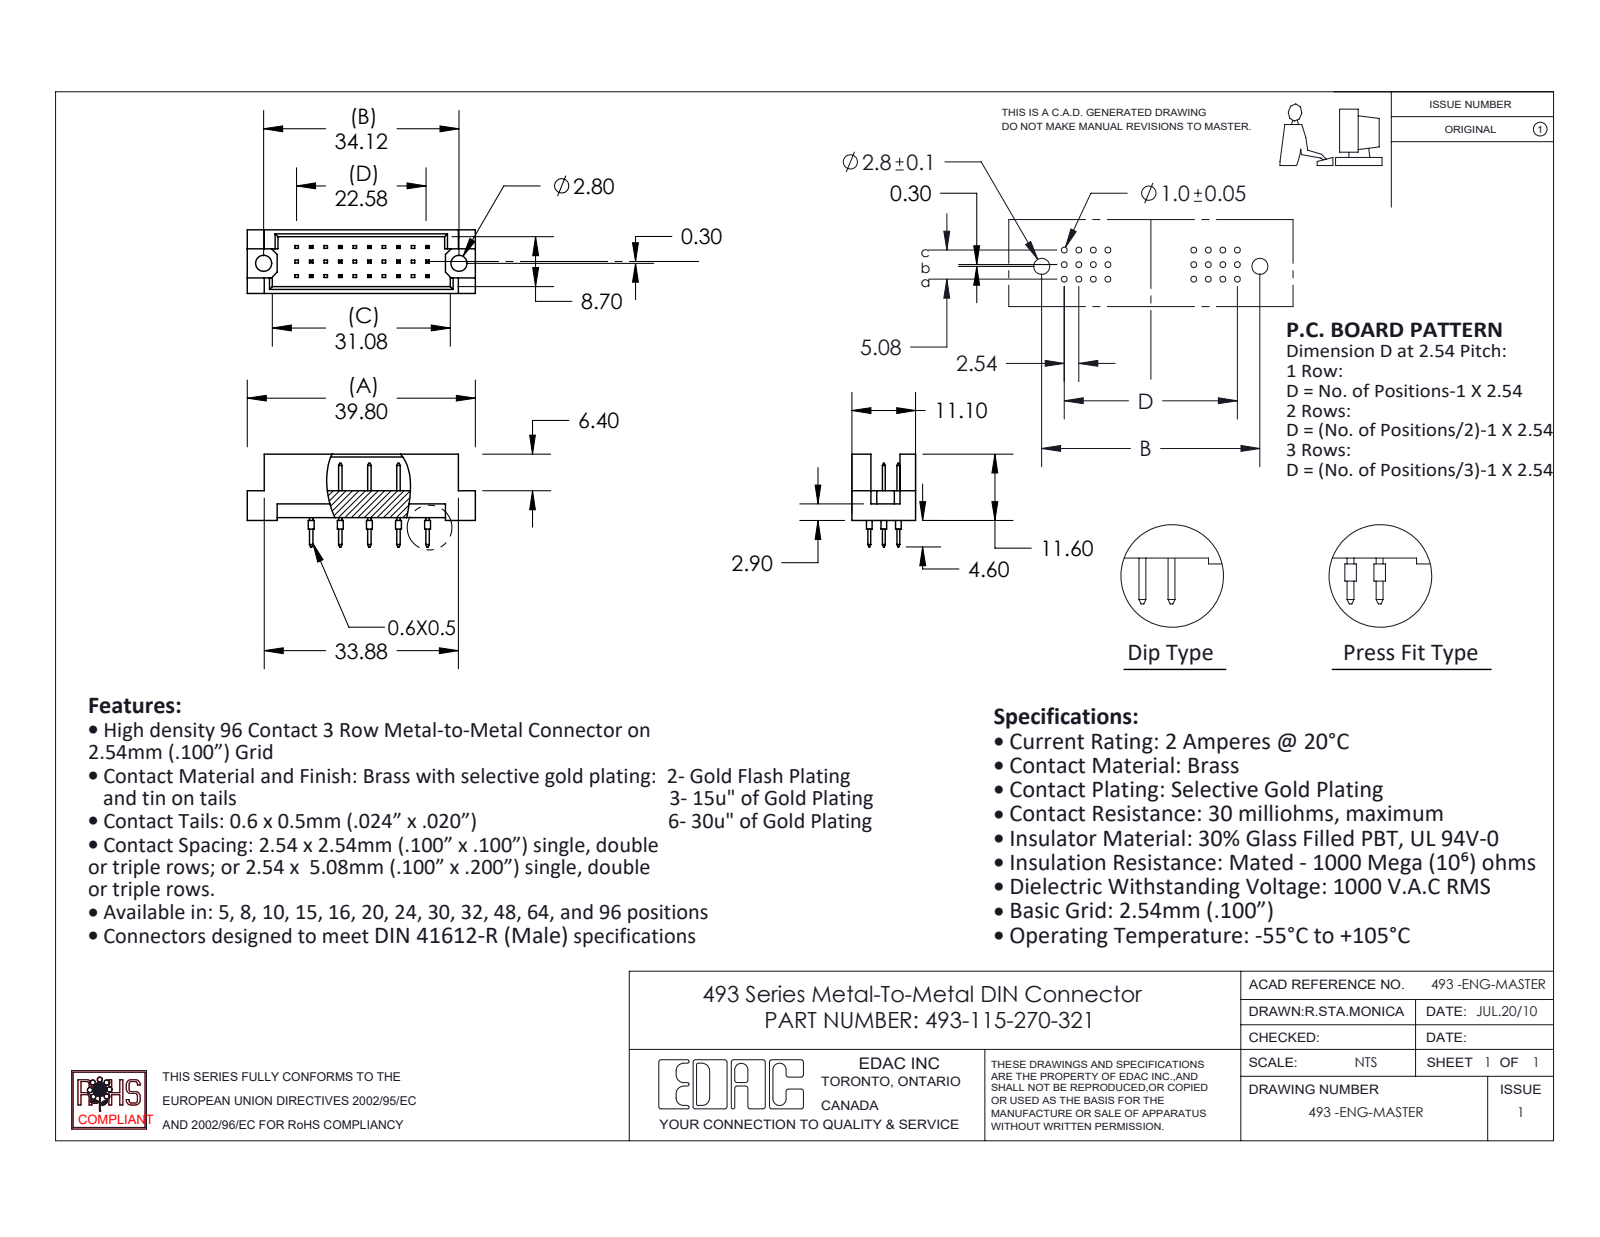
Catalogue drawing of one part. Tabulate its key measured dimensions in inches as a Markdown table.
| quantity | value |
| --- | --- |
| part name | 493-290_70; 493-115-270-321; 493 Part_30 |
| STEP written by | SolidWorks 2020 (CONFIG_CONTROL_DESIGN) |
| units | inches |
| bodies | 16 solids, 502 faces (468 planar, 34 cylindrical, 0 other) |
| overall size | 1.567 × 0.638 × 0.437 |
| volume | 0.149 in³ |
| surface area | 5.038 in² |
| round holes (diameter × count) | 0.11 × 2 |
| round bosses / shafts (diameter × count) | 0.039 × 15 |
| main face-to-face distances | 0.047, 0.39, 0.437, 0.2, 0.02, 0.343, 0.1, 0.185, 0.4, 0.094 |
| hole center spacings | 1.343 |
